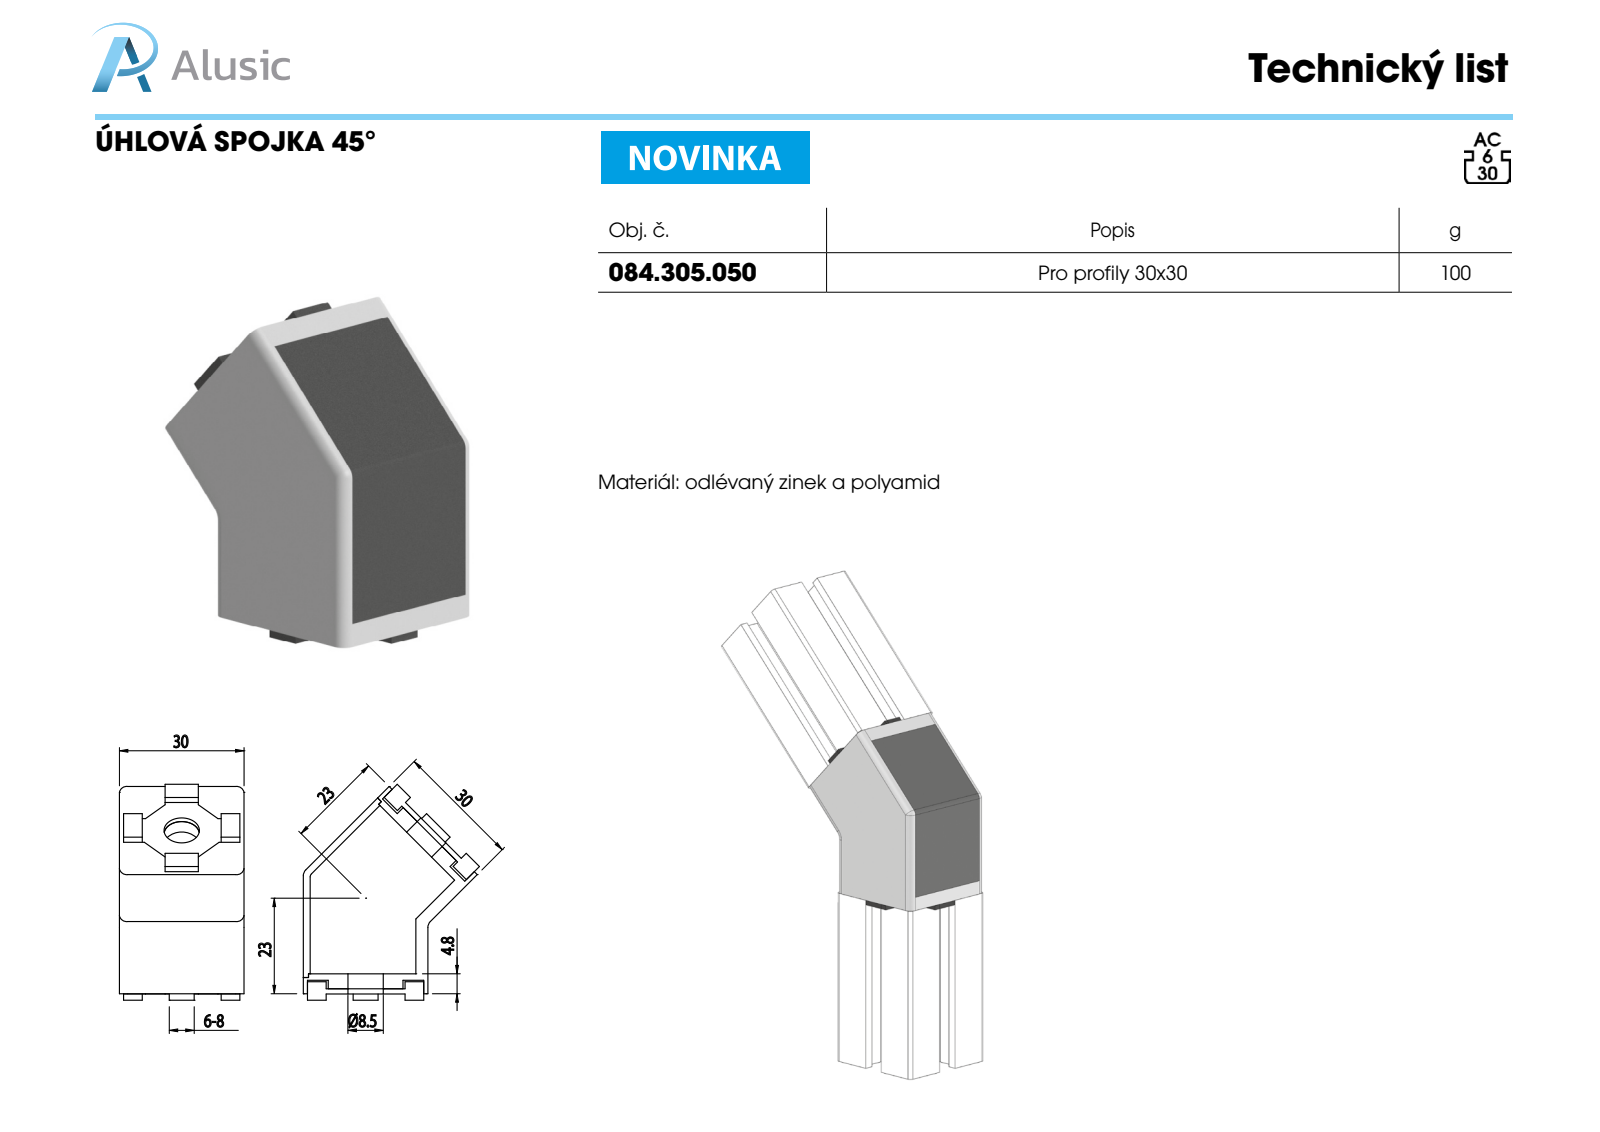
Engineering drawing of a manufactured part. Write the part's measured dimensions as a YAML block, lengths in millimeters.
part_name: "084.305.050A; 084.305.050B; 084.305.050; 084.305.050C"
step_written_by: "SolidWorks 2018 (AUTOMOTIVE_DESIGN)"
units: millimeters
bodies: {solids: 4, faces: 256, planar: 230, cylindrical: 22, other: 4}
overall_size: [51.97, 42.41, 30]
volume: 18366
surface_area: 16273
round_holes:
  - {diameter: 8.5, count: 3}
partial_cylinders:
  - {radius: 2, count: 10}
  - {radius: 0.75, count: 1}
  - {radius: 1, count: 1}
face_to_face_distances: [2.9, 27.1, 30, 4.8, 24.2, 1.65, 1.2, 3.6, 1, 1.25]
